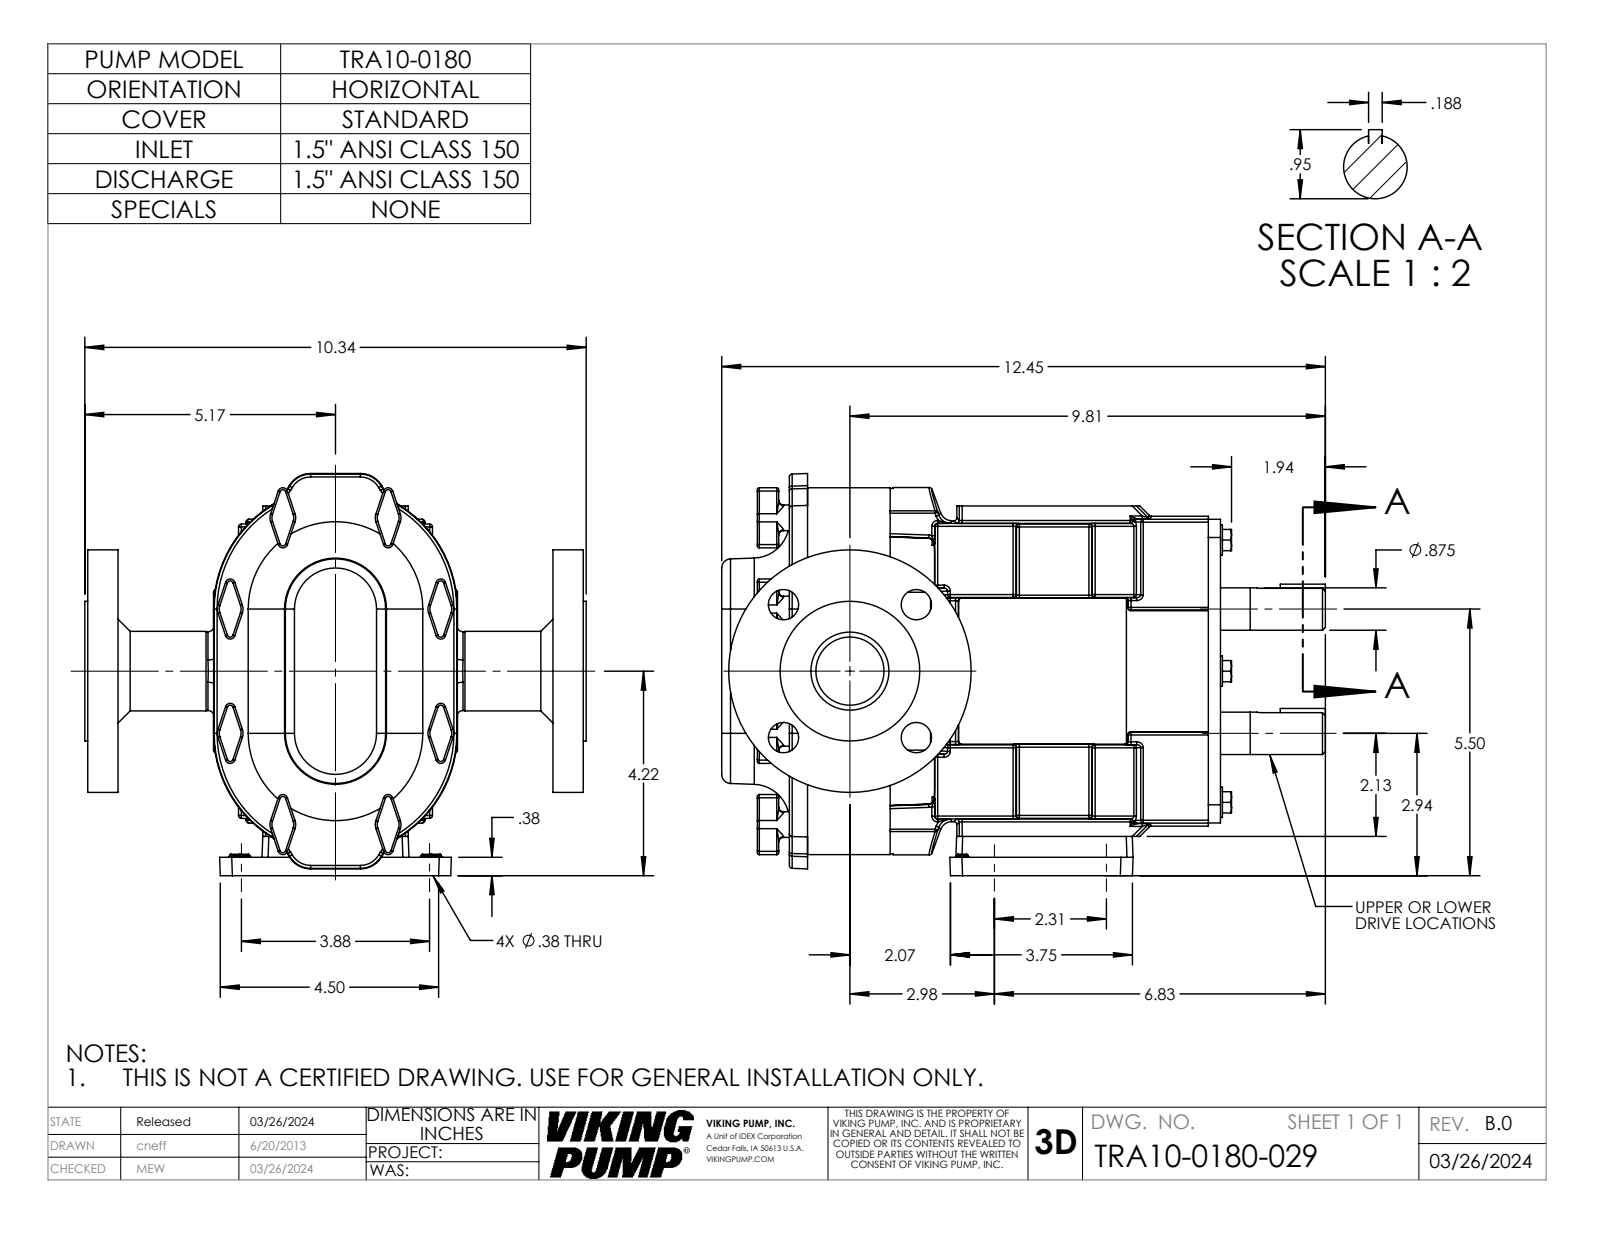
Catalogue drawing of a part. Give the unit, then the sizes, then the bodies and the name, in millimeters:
Units: millimetres
Overall size (bounding box): 316.2 × 262.6 × 210.6
Round holes (diameter × count): ⌀9.5 ×4, ⌀15.9 ×4, ⌀35.7 ×1, ⌀40.9 ×1
Round bosses / shafts (diameter × count): ⌀13.5 ×8, ⌀15.9 ×6, ⌀22.2 ×2, ⌀127 ×1, ⌀73.2 ×1, ⌀41.7 ×1, ⌀41.3 ×1
Partial cylindrical surfaces — rounded edges, fillets, slot ends (radius × count): R1.5 ×189, R1 ×64, R3.2 ×20, R0.8 ×16, R2.5 ×16, R6.4 ×14, R9.5 ×4, R12.7 ×4
Main face-to-face distances: 43.3, 15.9, 75.8, 167.9, 243.7, 59.9, 183.8, 216.3, 173.1, 9.5
Hole centre spacings: 49.2, 69.6, 58.7, 98.4, 98.6, 114.7
Volume: 4 429 000 mm³ · Surface area: 394 800 mm²
Bodies: 5 solids, 1207 faces (321 planar, 469 cylindrical, 417 other)
Part name (STEP PRODUCT): TRA10-0180-029; TRA10-0180-BODY; TRA10-0150-COVER-STD; 0300FLG150-15 (+1 more)
STEP written by: SolidWorks 2022 (AUTOMOTIVE_DESIGN)
